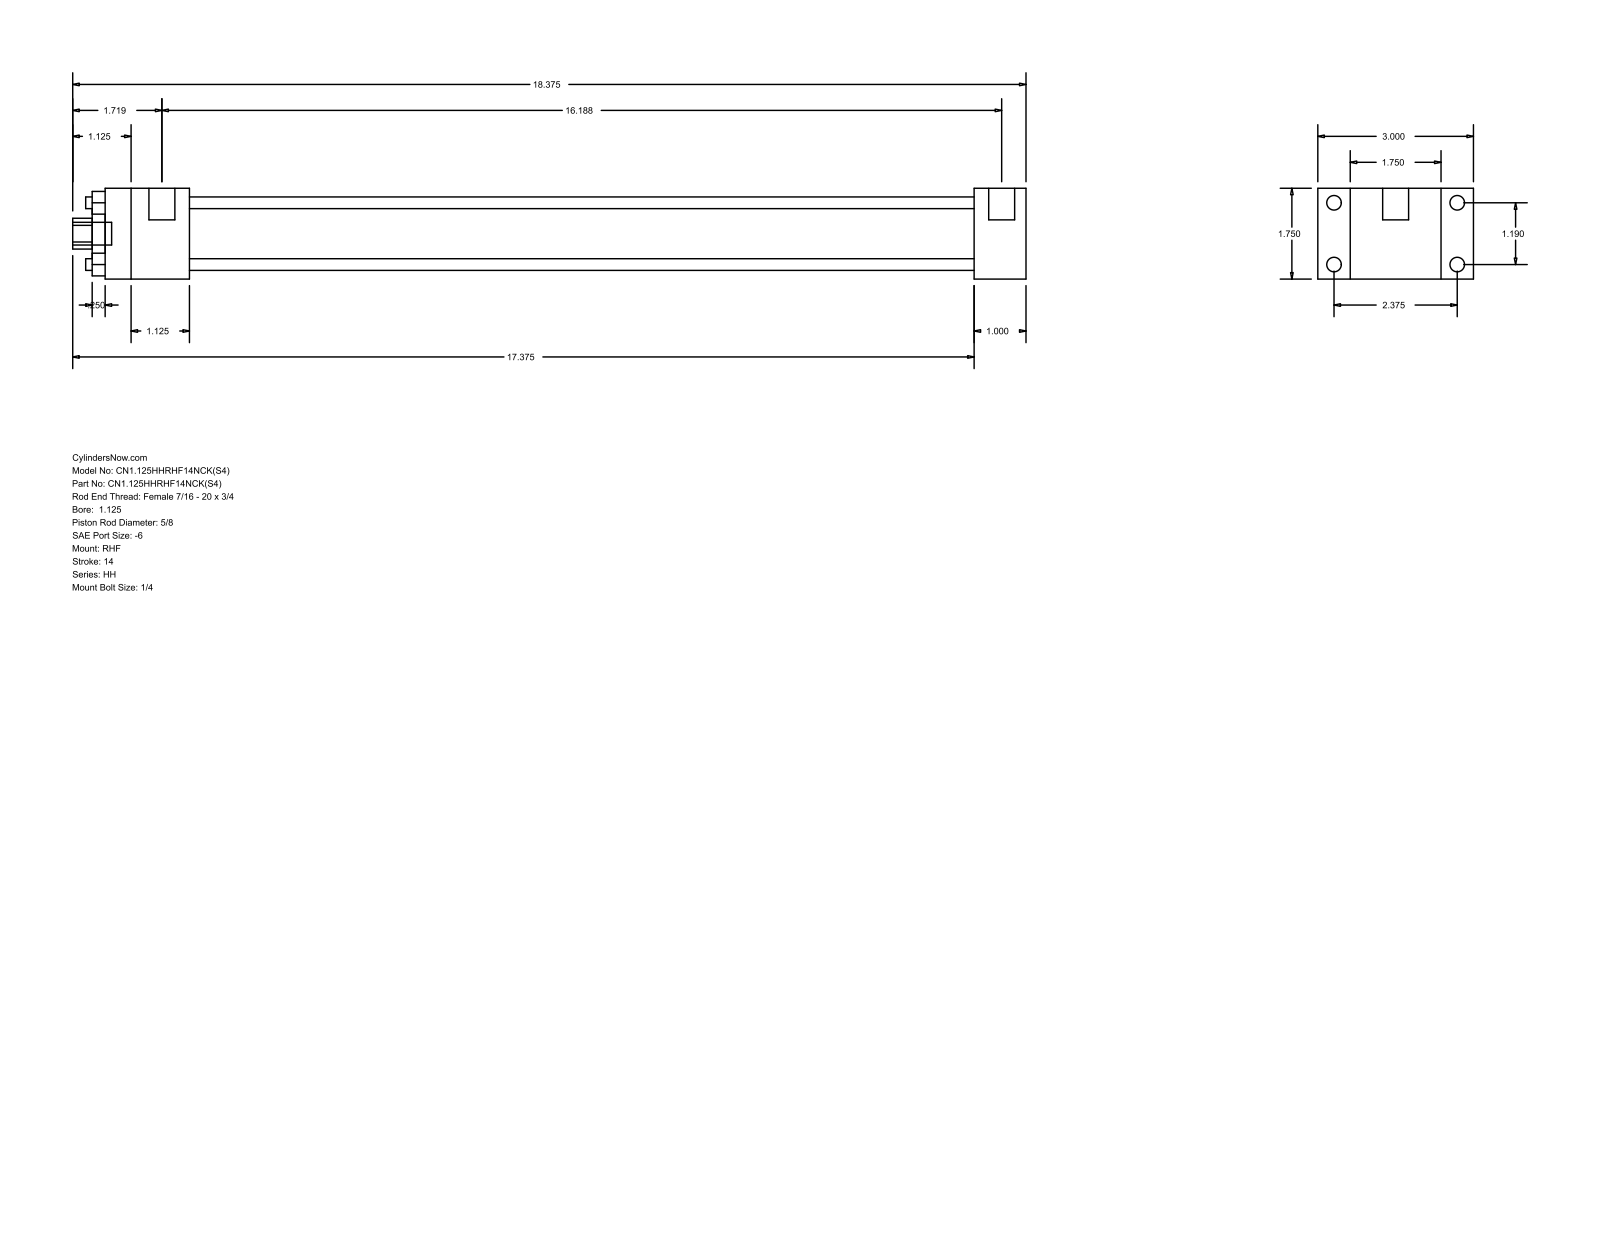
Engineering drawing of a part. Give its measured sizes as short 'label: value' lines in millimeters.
name: HH_RHF__0112_0.625
written by: GSSL Pune (CONFIG_CONTROL_DESIGN)
unit: mm
bodies: 0 solids, 88 faces (60 planar, 28 cylindrical, 0 other)
size: 466.73 × 76.2 × 44.45
holes: 4× ⌀5.71, 1× ⌀15.88, 1× ⌀28.57, 1× ⌀34.92
bosses: 4× ⌀7.14, 4× ⌀5.56, 2× ⌀12.7, 1× ⌀11.11
rounds: 1× R7.54
face distances: 44.46, 15.87, 60.33, 25.41, 76.2, 384.17, 409.58, 41.27, 425.44, 450.85
hole spacings: 21.37, 30.22, 42.74
